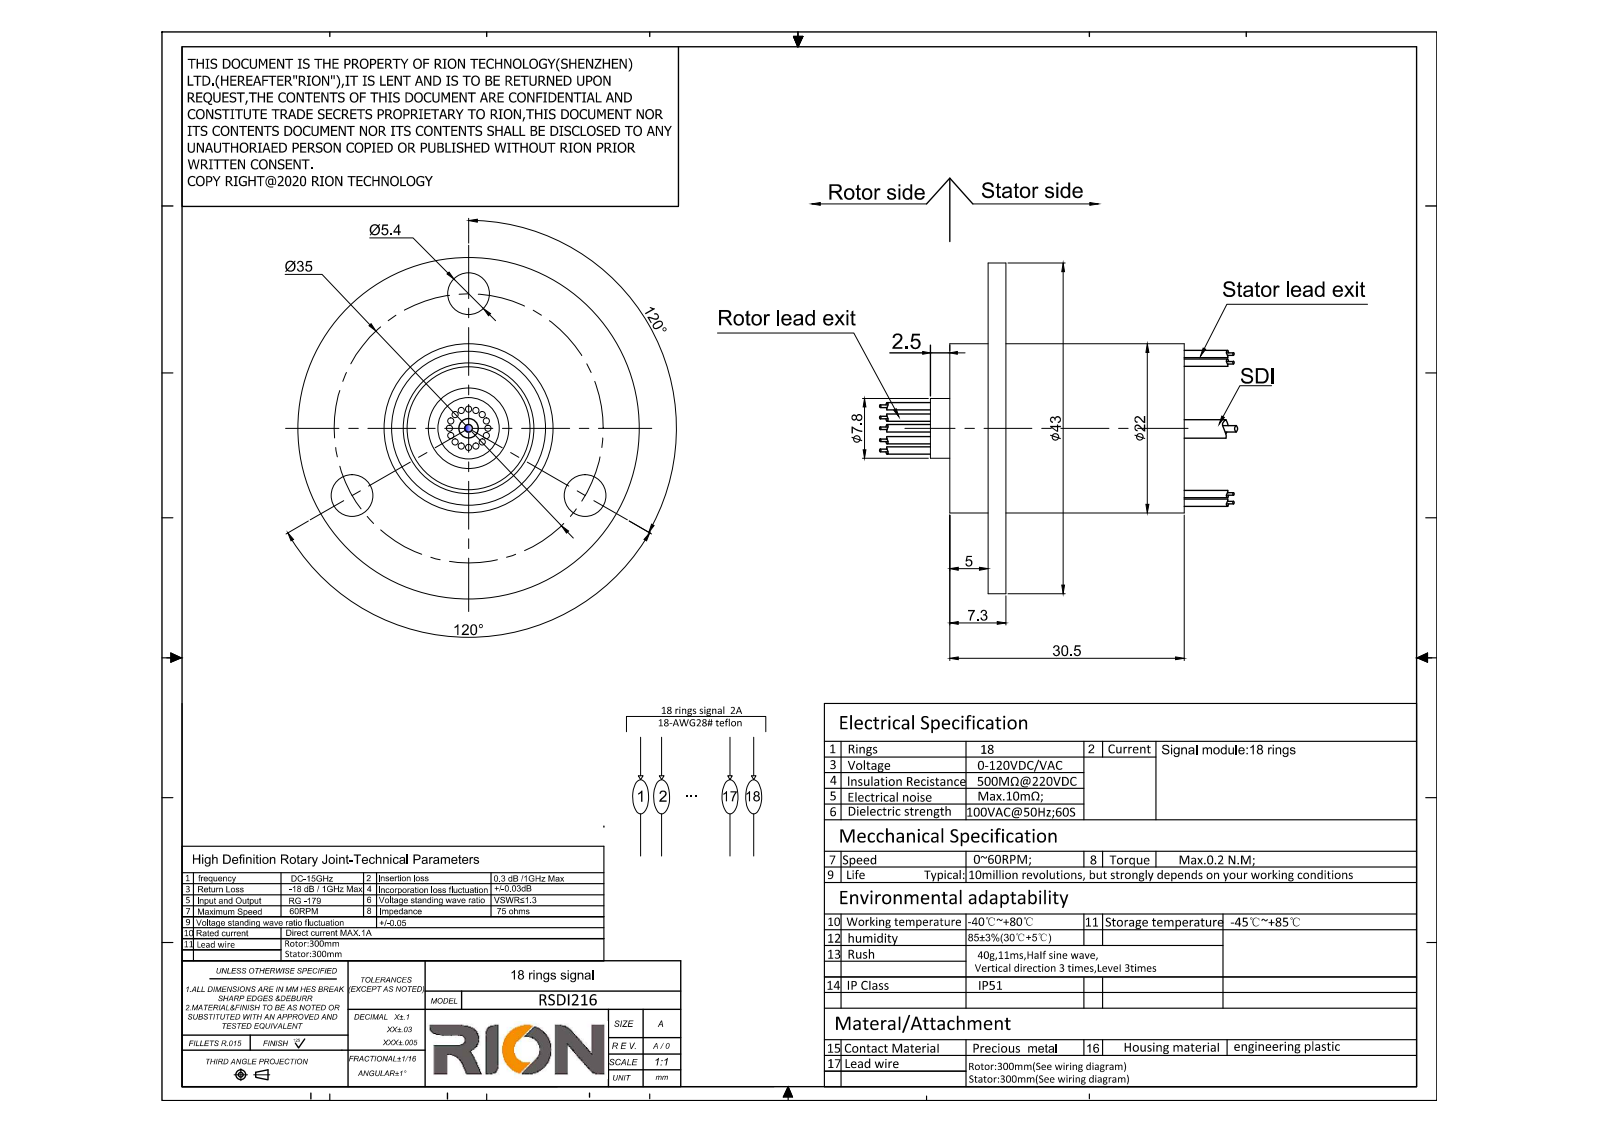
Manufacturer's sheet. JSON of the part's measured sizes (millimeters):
{"part_name": "MSDI216", "step_written_by": "SolidWorks 2014 (CONFIG_CONTROL_DESIGN)", "units": "millimeters", "bodies": {"solids": 1, "faces": 133, "planar": 43, "cylindrical": 90, "other": 0}, "overall_size": [79.4, 43, 43], "volume_mm3": 14687, "surface_area_mm2": 7683, "round_holes": [[5.4, 3]], "round_bosses_or_shafts": [[0.8, 36], [43, 1], [22, 1], [7.8, 1], [2.6, 1]], "face_to_face_distances": [2.3, 23.2, 25.5, 5, 7.3, 30.5, 33, 2.5, 7.5, 9.8], "hole_center_spacings": [30.31, 30.32]}
